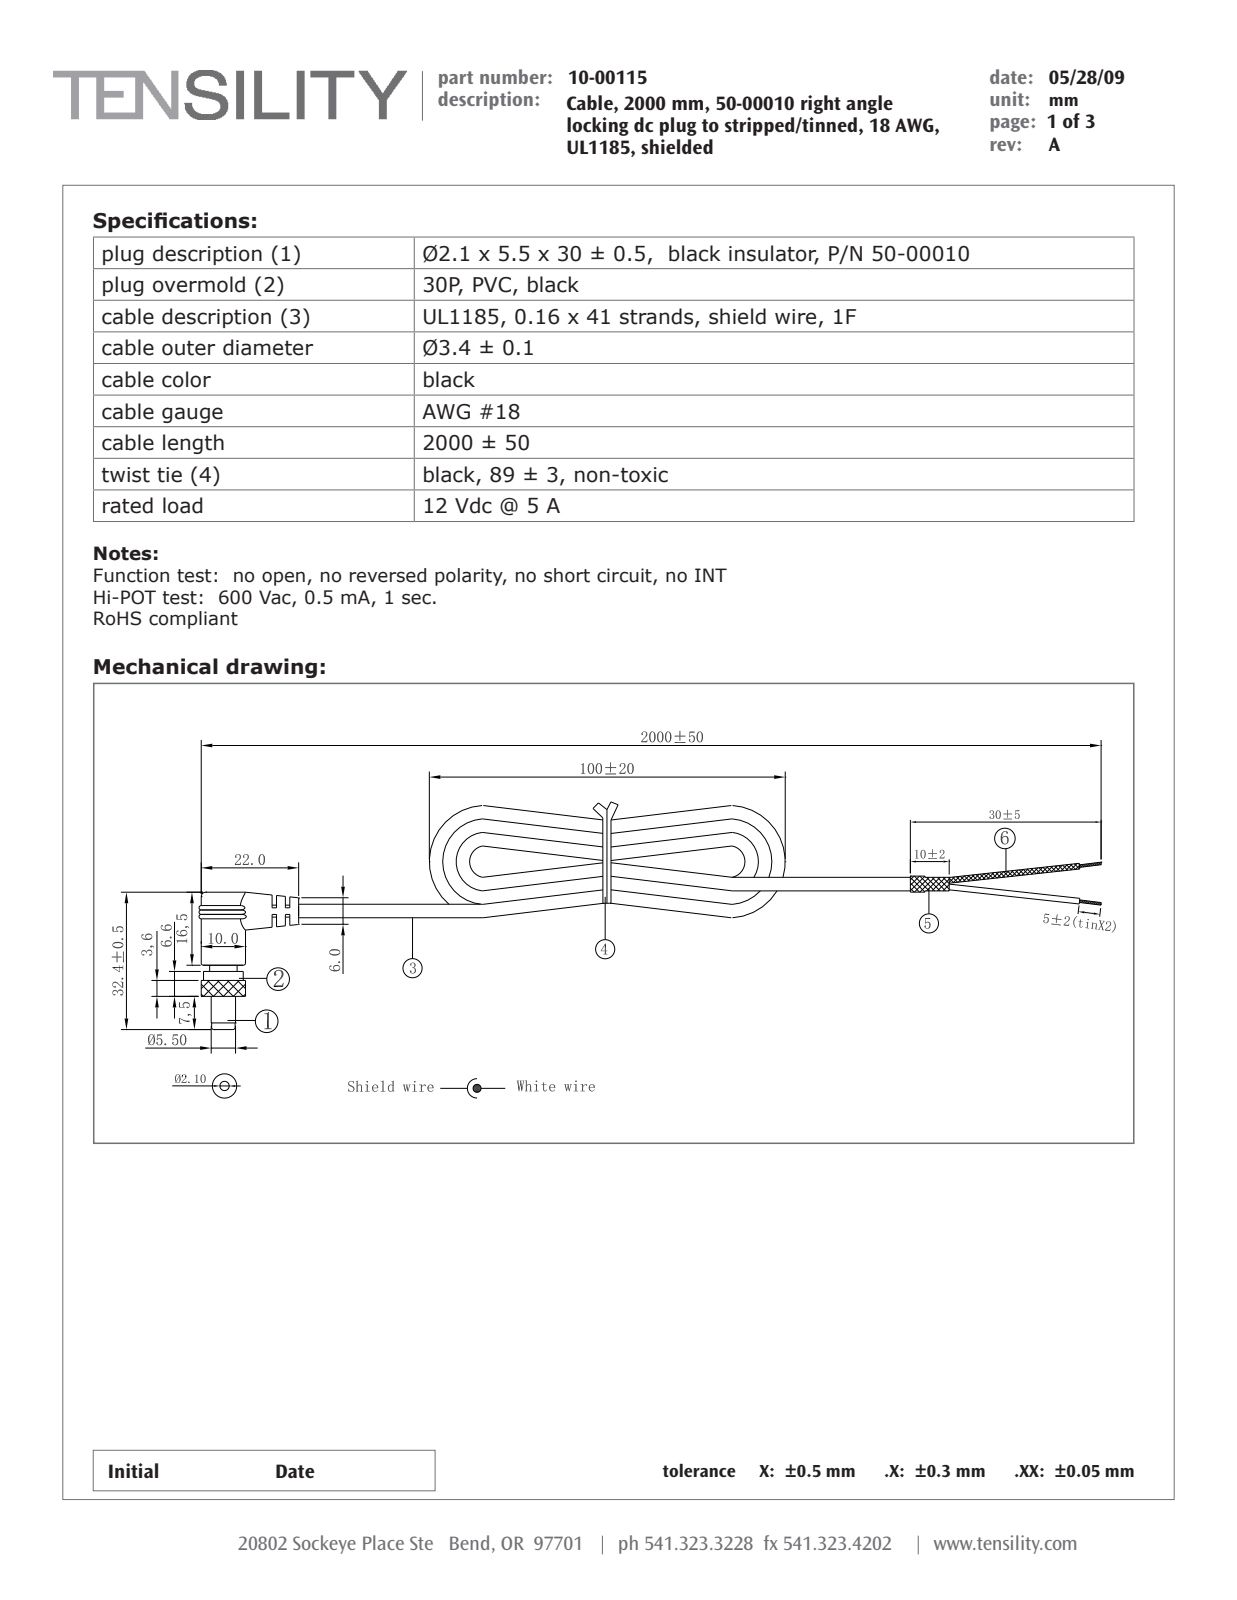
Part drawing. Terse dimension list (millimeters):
name: 50-00010 shell 2; 50-00010; 24-00017; 50-00010 insulator (+6 more)
written by: SolidWorks 2015 (CONFIG_CONTROL_DESIGN)
unit: mm
bodies: 93 solids, 2124 faces (793 planar, 463 cylindrical, 868 other)
size: 191.5 × 32.4 × 11
volume: 3 337 mm³; area: 7 324 mm²
holes: 1× ⌀1.6, 1× ⌀2.1, 1× ⌀2.16, 1× ⌀2.4, 1× ⌀2.6, 1× ⌀2.85, 1× ⌀3.85, 1× ⌀5.04, 1× ⌀5.44, 1× ⌀5.5, 1× ⌀5.65, 1× ⌀6.4
bosses: 1× ⌀11, 1× ⌀10, 1× ⌀8.5, 1× ⌀7, 1× ⌀6.2, 1× ⌀6, 1× ⌀5.48, 1× ⌀5.3
rounds: 2× R0.75
face distances: 3, 1, 2, 16.5, 8.4, 24.9, 5, 10, 1.8, 6.6
